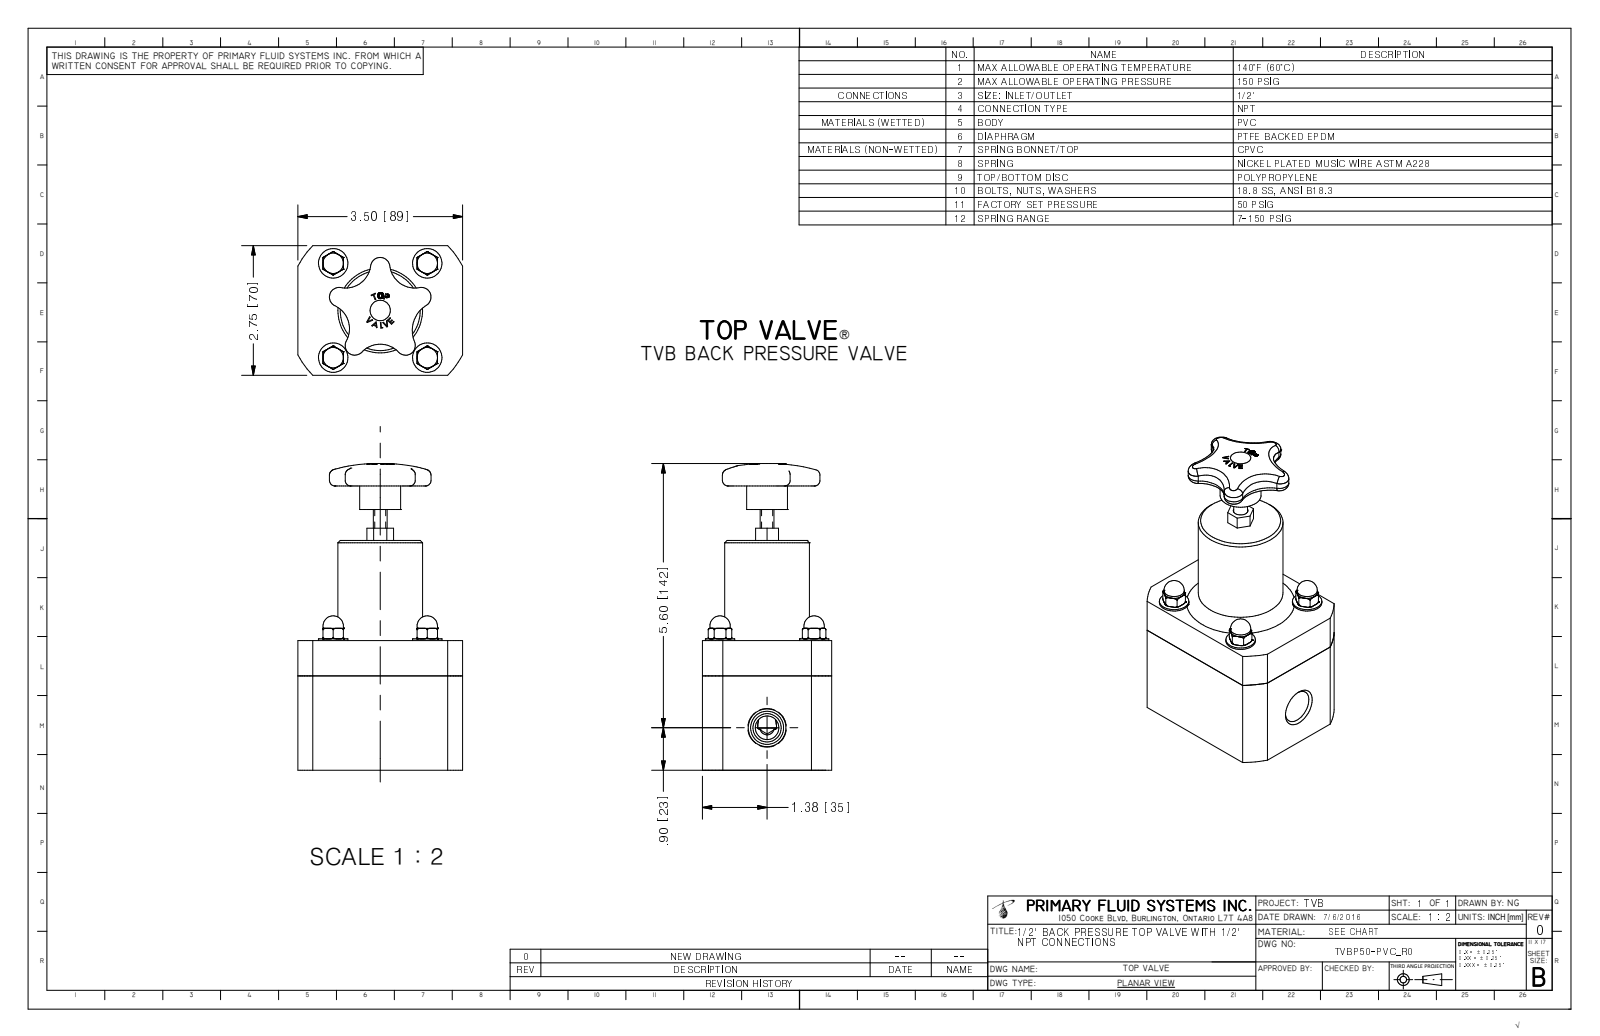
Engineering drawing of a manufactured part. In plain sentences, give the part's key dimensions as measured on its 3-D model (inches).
The part is named "TVBP50-PVC_R0". Its 3-D file was written by "Autodesk Inventor 2009 (AUTOMOTIVE_DESIGN)". It is 1 solid with 339 faces: 145 planar, 46 cylindrical and 148 other. Overall it measures 6.502 by 3.5 by 2.75 inches. Its volume is 32.19 cubic inches and its surface area 81.72 square inches. Round holes: 4 of diameter 0.175, 1 of diameter 0.313, 1 of diameter 0.703. Round bosses or shafts: 4 of diameter 0.625, 4 of diameter 0.433, 4 of diameter 0.375, 1 of diameter 1.8, 1 of diameter 0.87, 1 of diameter 0.293. Partial cylindrical surfaces (rounded edges, fillets, slot ends): 5 of radius 0.085, 5 of radius 0.205, 4 of radius 0.536, 4 of radius 0.656, 1 of radius 0.625, 1 of radius 0.745, 1 of radius 1.988. The main face-to-face distances are 2.75, 3.5, 2.75, 4.875, 2.125, 0.7, 2.8, 0.433, 2.786, 0.036. The hole center spacings are 1.414, 2, 2.828.
